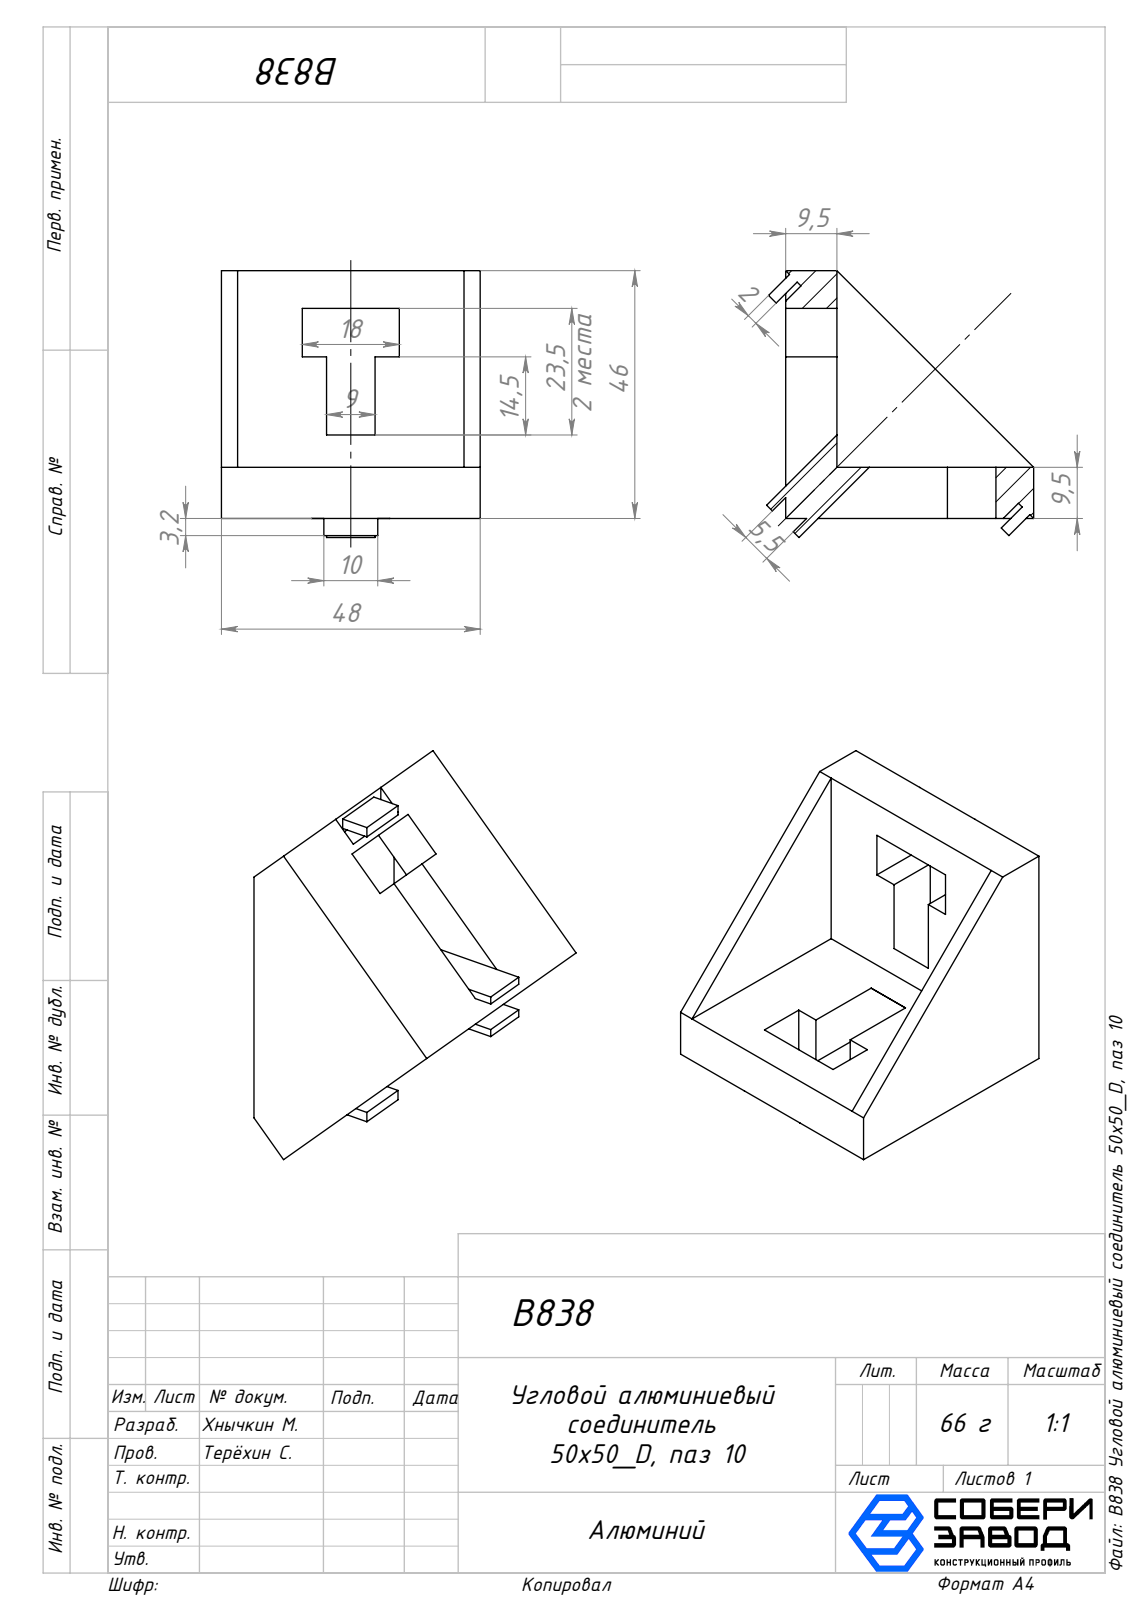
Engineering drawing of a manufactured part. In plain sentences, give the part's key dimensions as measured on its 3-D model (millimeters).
The part is named "B838 Угловой алюминиевый соединитель 50х50_D, паз 10". Its 3-D file was written by "SolidWorks 2025 (AUTOMOTIVE_DESIGN)". It is 1 solid with 54 faces: 54 planar, 0 cylindrical and 0 other. Overall it measures 49.54 by 49.54 by 48 millimeters. Its volume is 35 349 cubic millimeters and its surface area 13 954 square millimeters. The main face-to-face distances are 9.5, 48, 3, 45, 46, 36.5, 19.5, 28.5, 16.5, 25.5.
